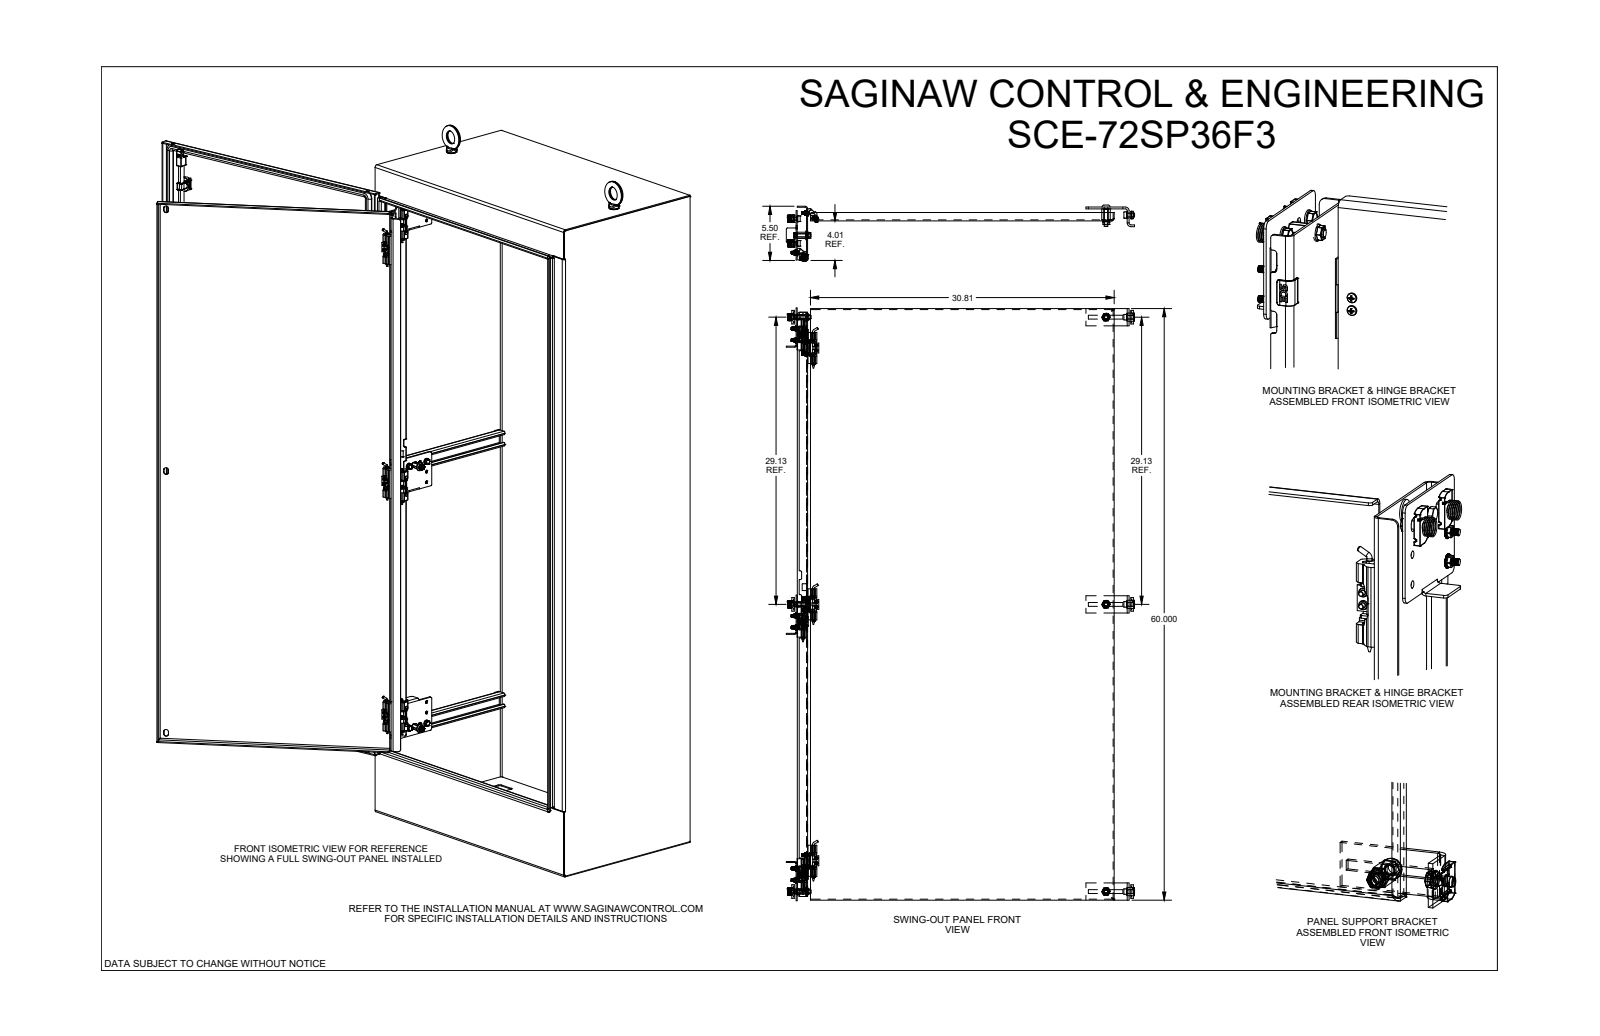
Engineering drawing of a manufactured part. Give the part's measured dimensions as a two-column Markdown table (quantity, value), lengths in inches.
| quantity | value |
| --- | --- |
| part name | SCE-72SP36F3 |
| STEP written by | SolidWorks 2021 (AUTOMOTIVE_DESIGN) |
| units | inches |
| bodies | 53 solids, 2490 faces (1213 planar, 926 cylindrical, 351 other) |
| overall size | 60.119 × 35.377 × 5.687 |
| volume | 267.5 in³ |
| surface area | 5 109 in² |
| round holes (diameter × count) | 0.25 × 18, 0.281 × 18, 0.36 × 12, 0.218 × 9, 0.04 × 6, 0.19 × 6, 0.156 × 3, 0.33 × 3, 0.383 × 3, 0.201 × 2, 0.375 × 2, 0.204 × 1 |
| round bosses / shafts (diameter × count) | 0.196 × 8, 0.34 × 6, 0.249 × 6, 0.886 × 3, 0.813 × 3, 0.5 × 3, 0.368 × 3, 0.31 × 3 |
| partial cylindrical surfaces (radius × count) | 0.011 × 54, 0.015 × 28, 0.188 × 28, 0.25 × 22, 0.1 × 18, 0.06 × 17, 0.03 × 16, 0.13 × 14 |
| main face-to-face distances | 0.104, 1.058, 1.385, 31.108, 32.166, 4.011, 5.396, 0.954, 1.162, 1.281 |
| hole center spacings | 0.592, 29.125, 26, 1.181, 25.625, 54.75, 2.098, 2.92 |
